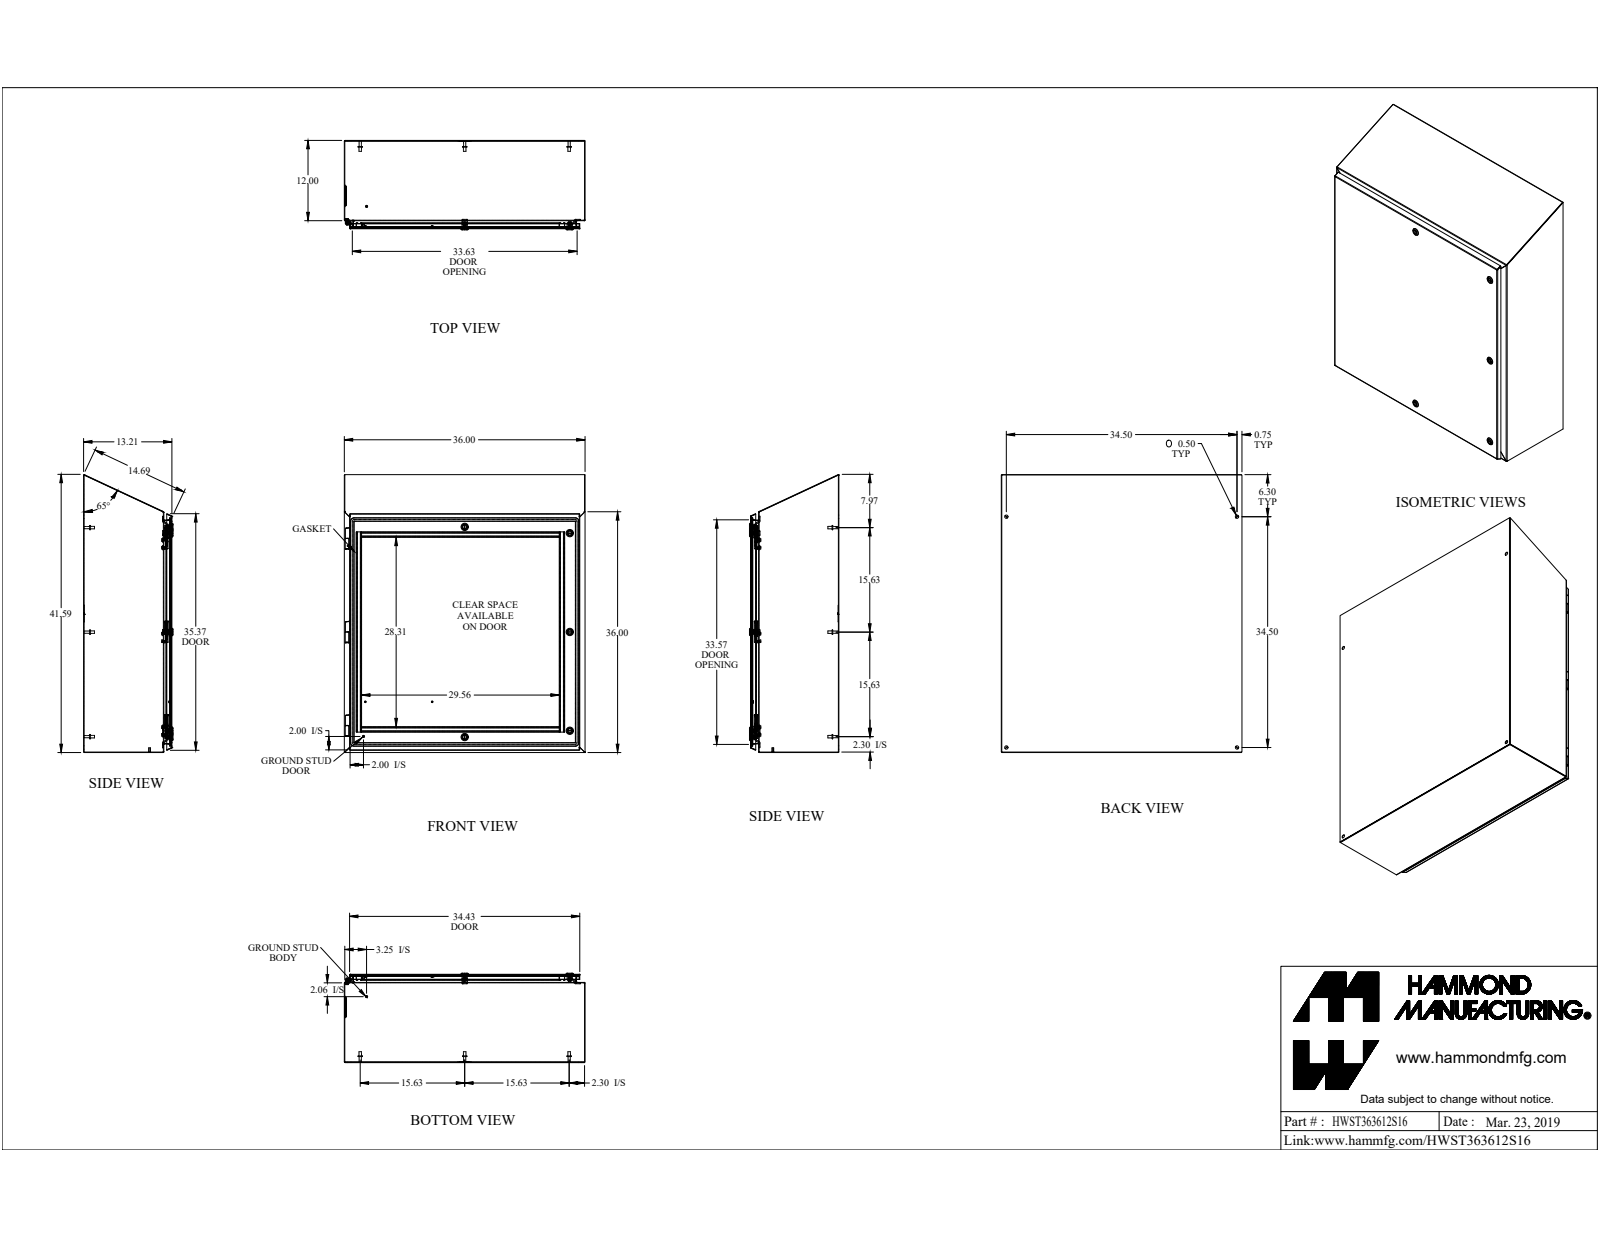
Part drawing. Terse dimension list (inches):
name: HWST363612S16
written by: SolidWorks 2019 (AUTOMOTIVE_DESIGN)
unit: in
bodies: 77 solids, 1767 faces (1094 planar, 482 cylindrical, 191 other)
size: 41.545 × 36 × 13.37
volume: 396.5 in³; area: 11 147 in²
holes: 12× ⌀0.194, 12× ⌀0.24, 9× ⌀0.5, 6× ⌀0.275, 5× ⌀0.197, 5× ⌀0.387, 5× ⌀0.63, 5× ⌀0.768, 2× ⌀0.13, 1× ⌀0.24, 1× ⌀3.5
bosses: 12× ⌀0.226, 11× ⌀0.625, 8× ⌀0.65, 8× ⌀0.375, 8× ⌀0.332, 6× ⌀0.236, 5× ⌀1.1, 5× ⌀0.785
rounds: 24× R0.039, 24× R0.043, 24× R0.25, 22× R0.125, 17× R0.036, 17× R0.108, 16× R0.012, 16× R0.03
face distances: 0.072, 0.072, 13.066, 13.138, 13.138, 13.21, 35.856, 35.928, 35.928, 36
hole spacings: 1.142, 13.987, 13.987, 27.974, 34.5, 1.142, 15.129, 12.845
